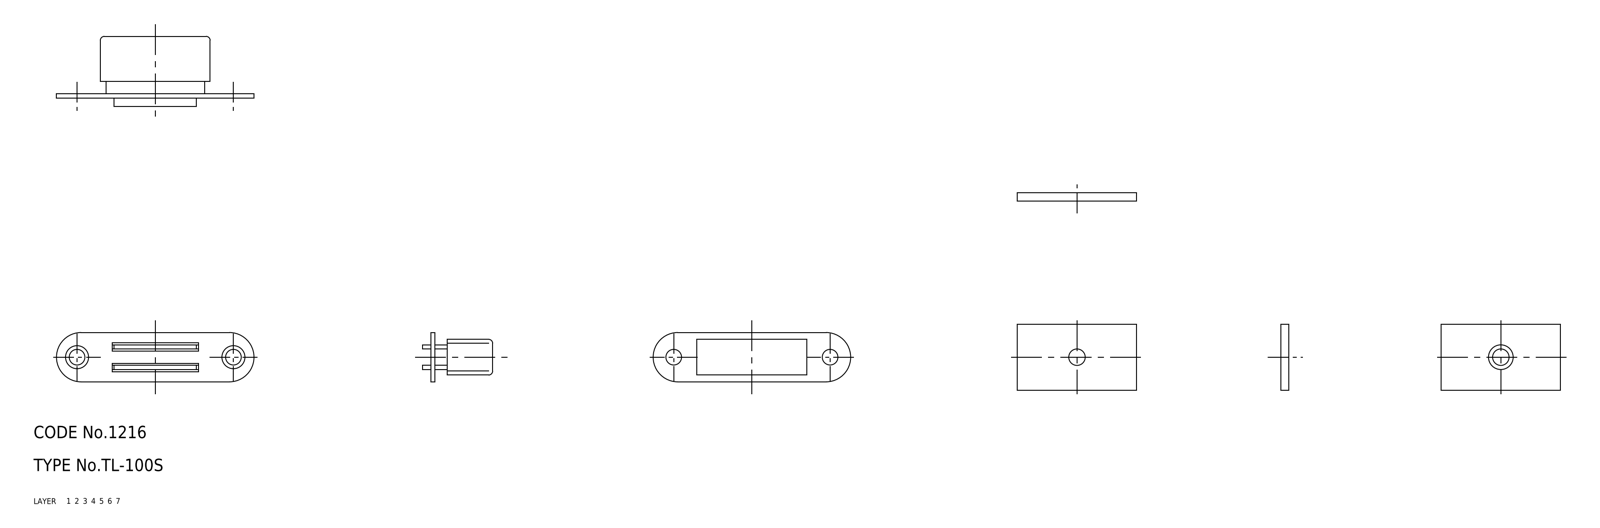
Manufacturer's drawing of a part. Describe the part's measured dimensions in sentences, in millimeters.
The part is named "67111595; 67111608; 67111621; 67111634 (+2 more)". Its 3-D file was written by "CADfix (AUTOMOTIVE_DESIGN)". It is 6 solids with 80 faces: 0 planar, 0 cylindrical and 80 other. Overall it measures 48 by 35.77 by 16 millimeters. Its volume is 3 599 cubic millimeters and its surface area 6 123 square millimeters.
